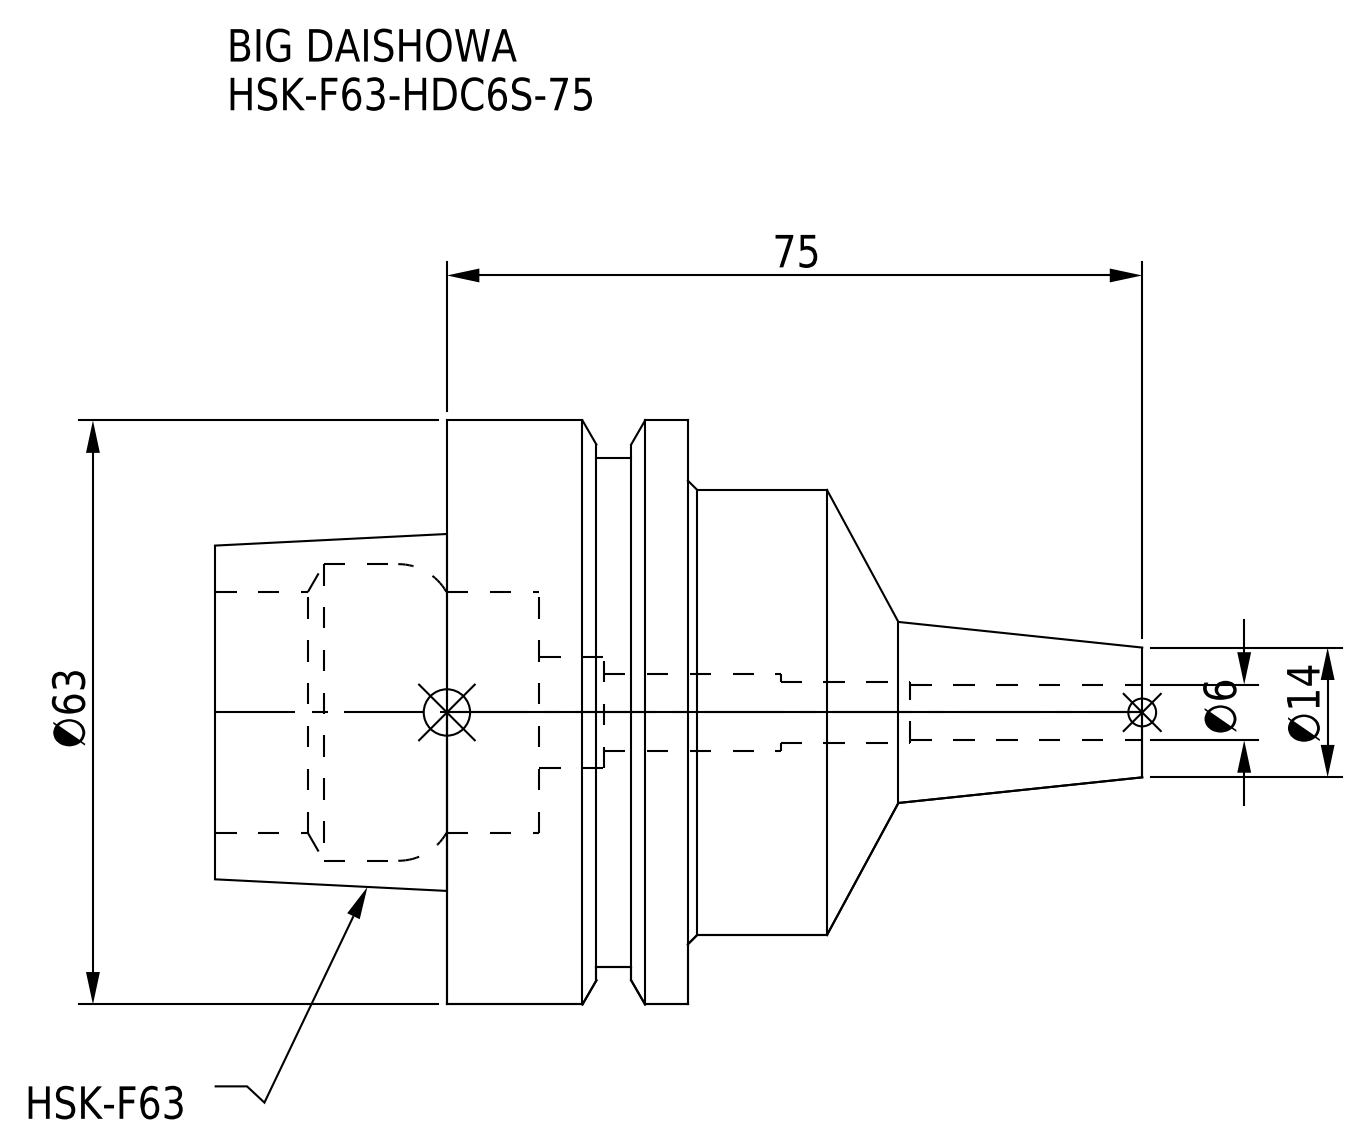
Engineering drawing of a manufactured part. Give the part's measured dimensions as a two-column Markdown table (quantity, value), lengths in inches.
| quantity | value |
| --- | --- |
| part name | HSK-F63-HDC6S-75 |
| STEP written by | CREO PARAMETRIC BY PTC INC, 2016380 (AUTOMOTIVE_DESIGN) |
| units | inches |
| bodies | 1 solid, 50 faces (10 planar, 24 cylindrical, 16 other) |
| overall size | 3.937 × 2.48 × 2.48 |
| volume | 7.335 in³ |
| surface area | 36.49 in² |
| round holes (diameter × count) | 0.236 × 1, 0.256 × 1, 0.325 × 1, 0.472 × 1, 1.024 × 1, 1.26 × 1 |
| round bosses / shafts (diameter × count) | 2.48 × 1, 2.165 × 1, 1.89 × 1 |
| main face-to-face distances | 1.024, 0.984, 2.008, 0.632, 0.392, 1.376, 0.783, 0.635, 0.241, 0.391 |
